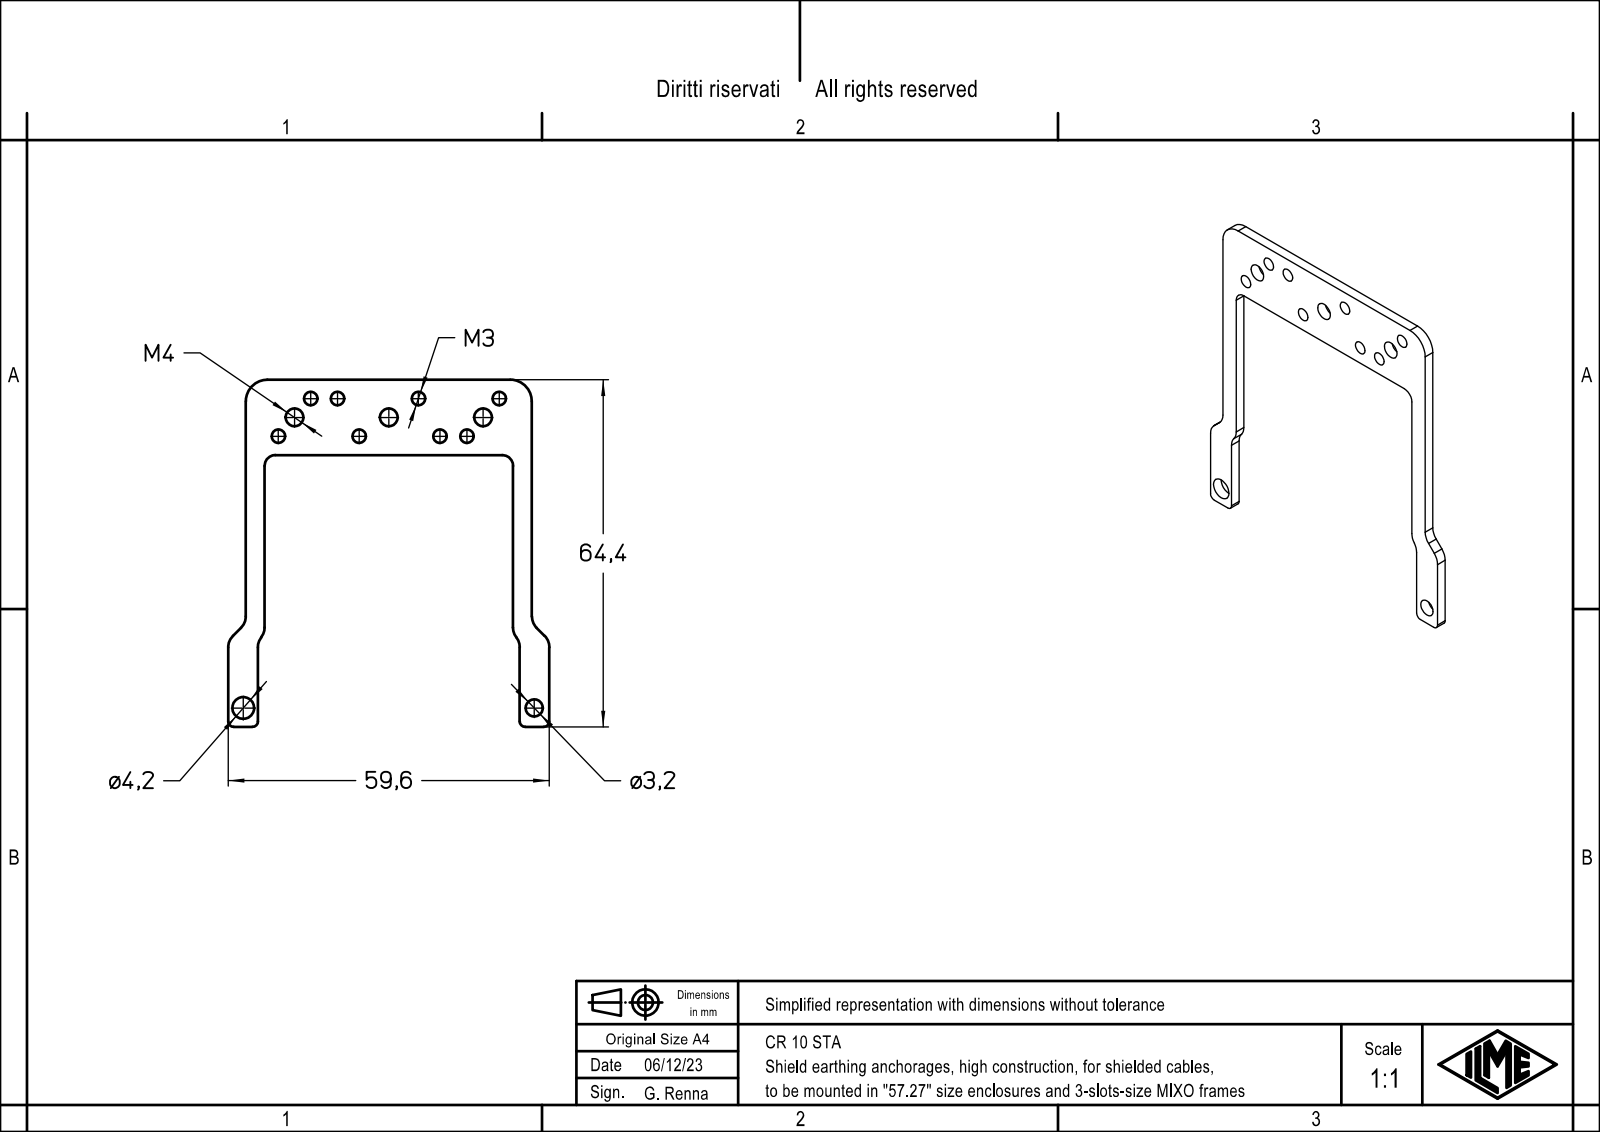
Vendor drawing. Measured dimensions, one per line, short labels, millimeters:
name: CR_10_STA
written by: Creo Elements/Direct Modeling 20.5B 27-May-2023 (C) Parametric Technology GmbH (AUTOMOTIVE_DESIGN)
unit: mm
bodies: 1 solid, 58 faces (16 planar, 42 cylindrical, 0 other)
size: 64.4 × 59.6 × 2
volume: 2 155 mm³; area: 3 060 mm²
holes: 8× ⌀2.5, 3× ⌀3.3, 1× ⌀3.2, 1× ⌀4.05
rounds: 8× R3, 4× R1, 2× R2, 2× R4
face distances: 2, 3.5, 49.6, 14, 53.1, 46.1, 3.25, 6.75, 52.85, 54.1
hole spacings: 4.61, 15, 13.04, 35, 5, 6.52, 8.06, 8.73
